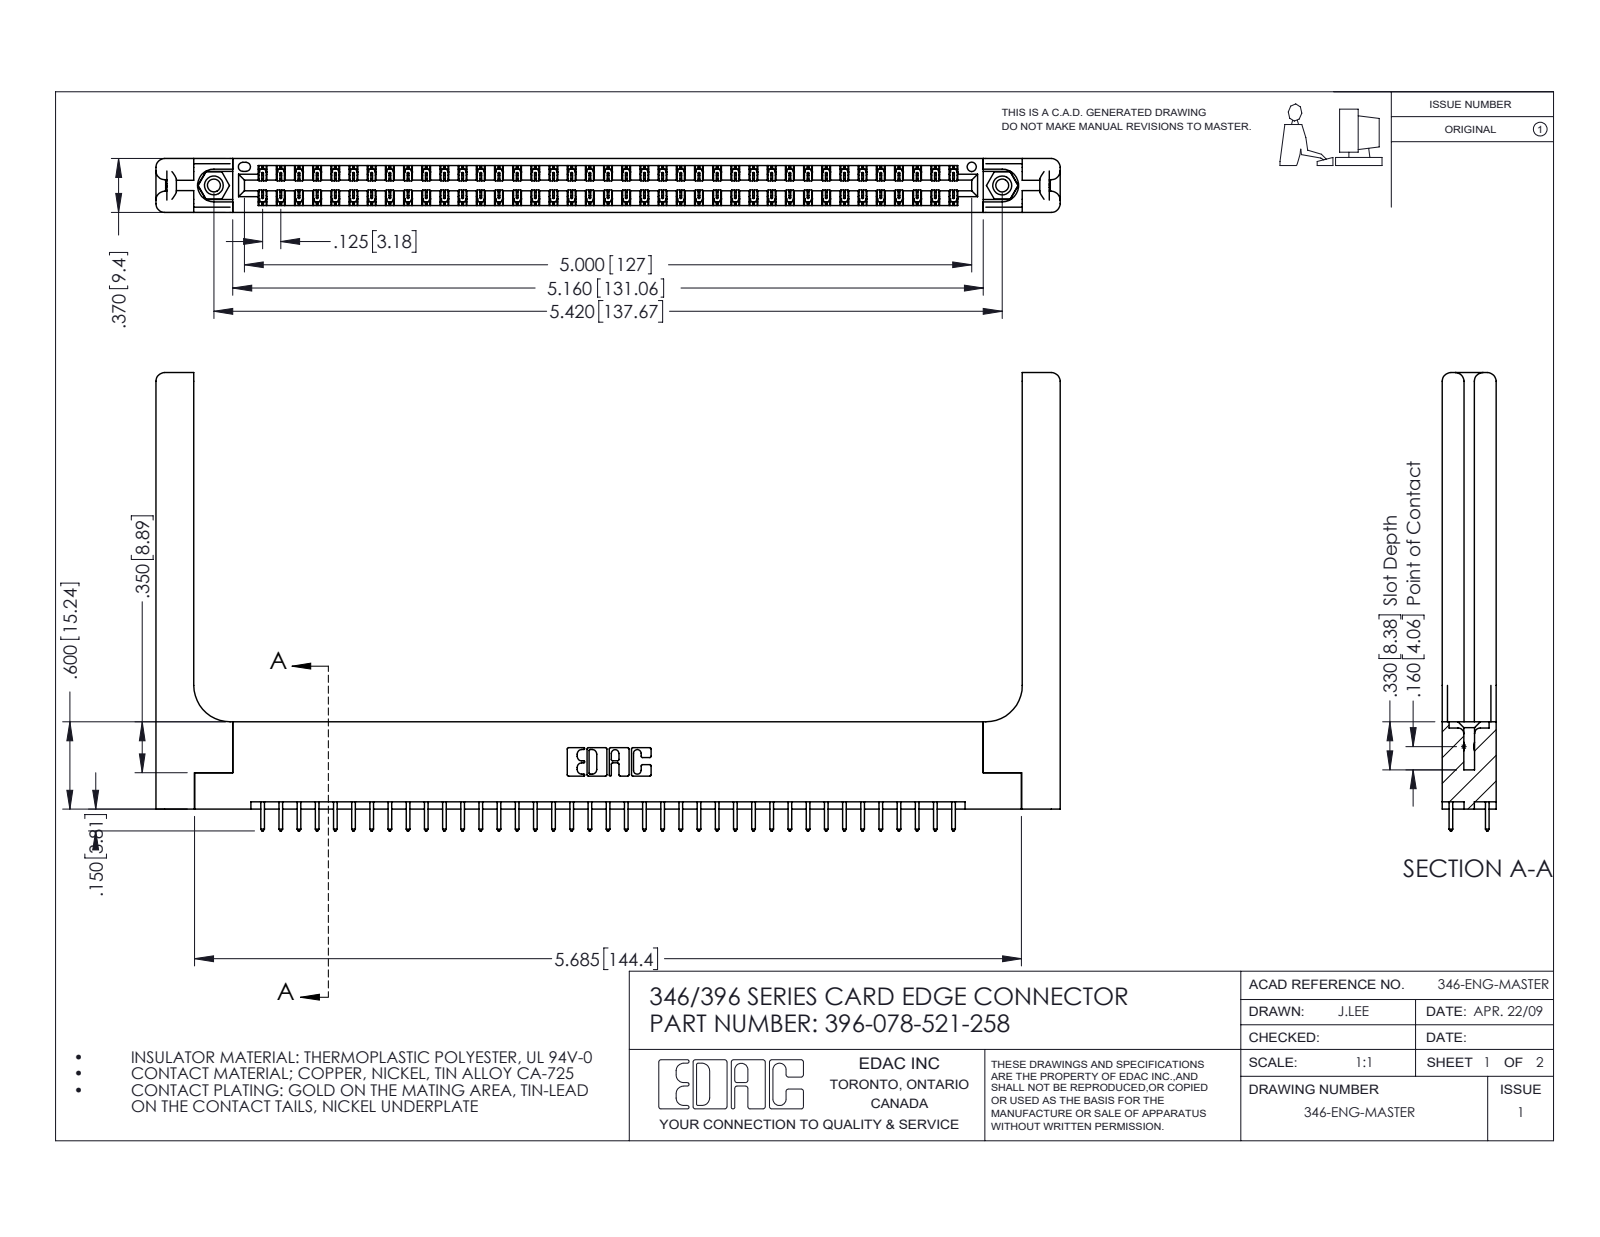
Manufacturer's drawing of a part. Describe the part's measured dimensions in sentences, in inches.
The part is named "346 Part_Flush Mounting Lugs - 0.156 Dia-TH; 346-220-058_345-220-058; 345-250-001_345-250-001-102; 345-292-001_345-293-121 (+1 more)". Its 3-D file was written by "SolidWorks 2016 (CONFIG_CONTROL_DESIGN)". It is 83 solids with 4434 faces: 2954 planar, 1420 cylindrical and 60 other. Overall it measures 6.216 by 3.15 by 0.37 inches. Its volume is 1.393 cubic inches and its surface area 39.99 square inches. Round holes: 2 of diameter 0.089, 2 of diameter 0.125, 2 of diameter 0.156, 1 of diameter 0.064. Round bosses or shafts: 2 of diameter 0.155. Partial cylindrical surfaces (rounded edges, fillets, slot ends): 117 of radius 0.006, 78 of radius 0.01, 22 of radius 0.01, 16 of radius 0.06, 6 of radius 0.007, 6 of radius 0.031, 3 of radius 0.026, 2 of radius 0.014. The main face-to-face distances are 0.37, 0.048, 0.322, 0.072, 0.25, 0.148, 0.15, 0.025, 0.298, 0.275. The hole center spacings are 0.246, 5.211, 5.42.
